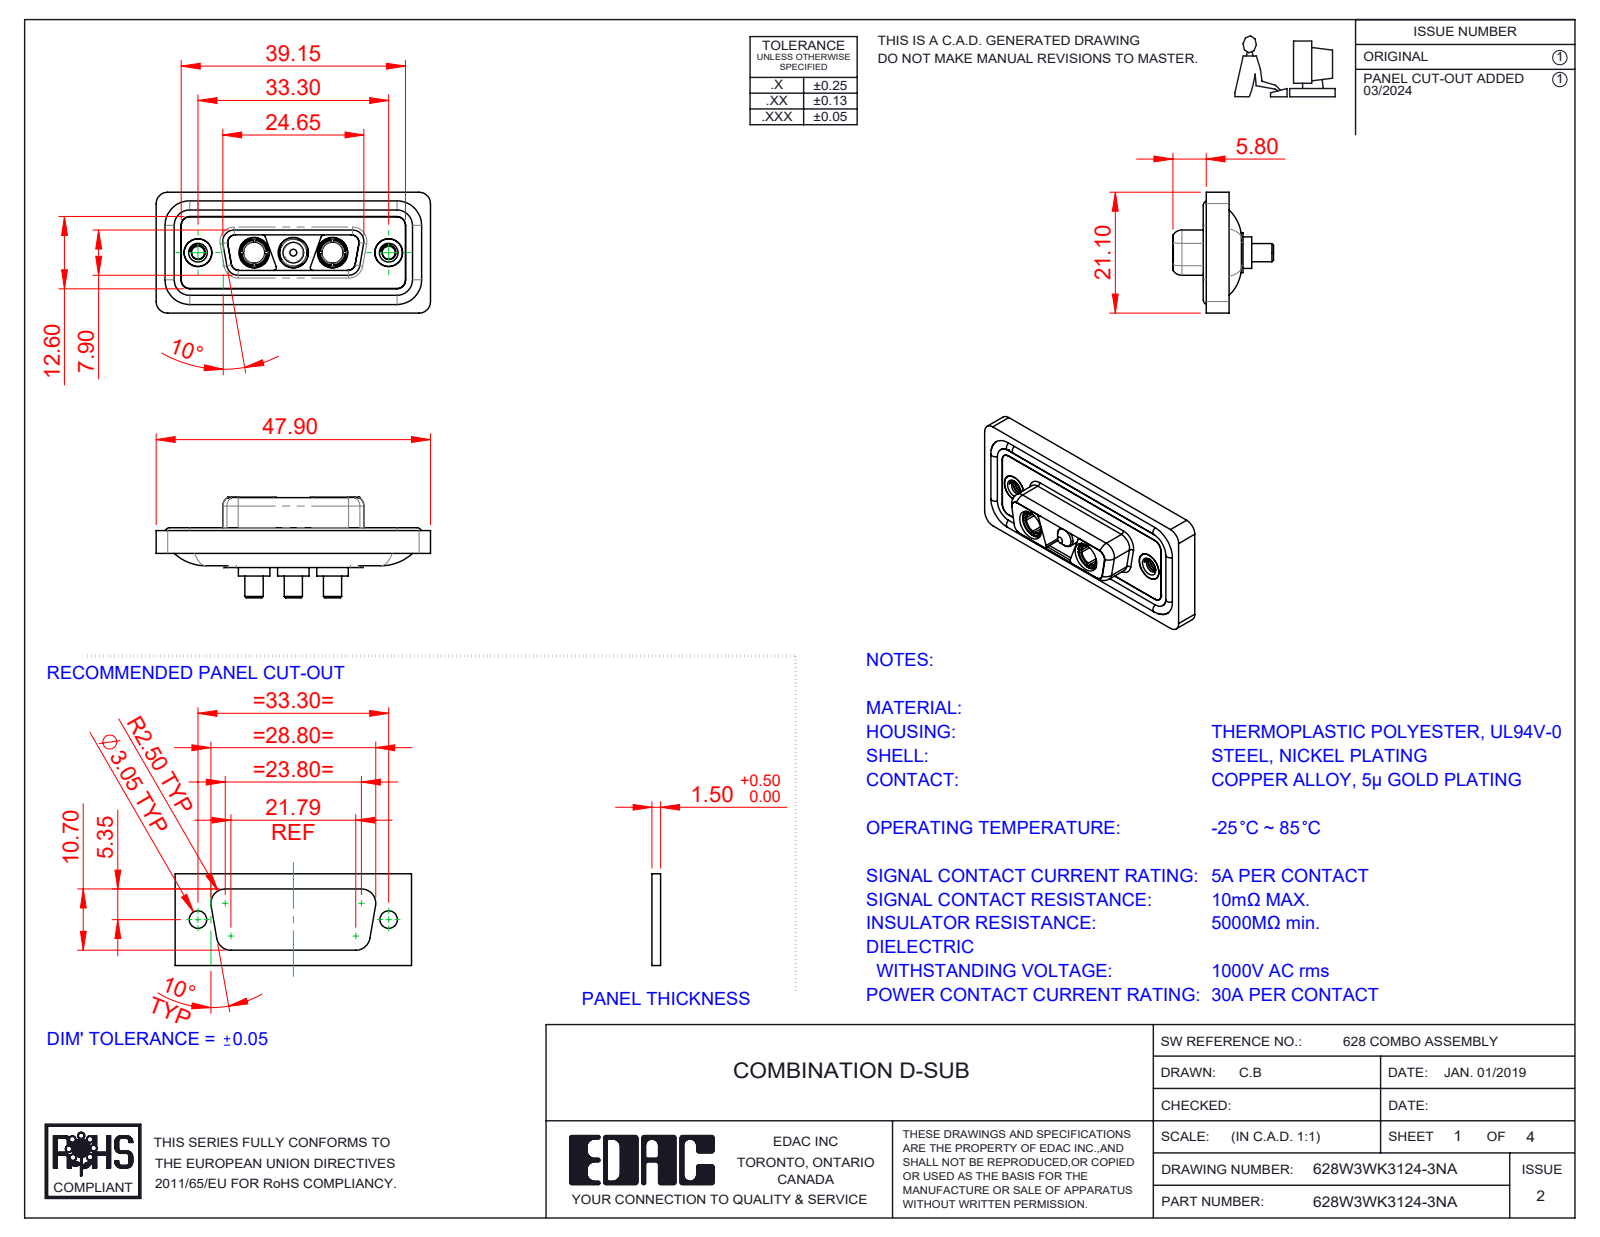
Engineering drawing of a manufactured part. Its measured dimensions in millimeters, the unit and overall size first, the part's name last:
Units: millimetres
Overall size (bounding box): 47.9 × 21.1 × 17.55
Round holes (diameter × count): ⌀4.85 ×5, ⌀5.3 ×3, ⌀2.26 ×2, ⌀3.7 ×2, ⌀4 ×2, ⌀4.05 ×2, ⌀5 ×2
Round bosses / shafts (diameter × count): ⌀1.6 ×4, ⌀5.5 ×3, ⌀5.2 ×3, ⌀4.75 ×3, ⌀3.75 ×3, ⌀3.2 ×3, ⌀4.96 ×2, ⌀4.95 ×2
Partial cylindrical surfaces — rounded edges, fillets, slot ends (radius × count): R1.5 ×22, R2 ×20, R1.35 ×12, R0.5 ×8, R1.6 ×8, R0.25 ×4, R0.6 ×4, R0.65 ×4
Main face-to-face distances: 0.4, 1.6, 0.5, 1.8, 1.1, 2.9, 5.65, 7.05, 5.35, 1.5
Hole centre spacings: 6.85, 9.8, 16.65, 23.5, 13.7, 33.3
Volume: 5 901 mm³ · Surface area: 9 516 mm²
Bodies: 13 solids, 581 faces (178 planar, 260 cylindrical, 143 other)
Part name (STEP PRODUCT): 628Combo Shell Front_15 Contacts; Power Pin_30A S; 628W3WK3124-3NA; 628Combo Housing_3WK3 (+4 more)
STEP written by: SolidWorks 2023 (CONFIG_CONTROL_DESIGN)
